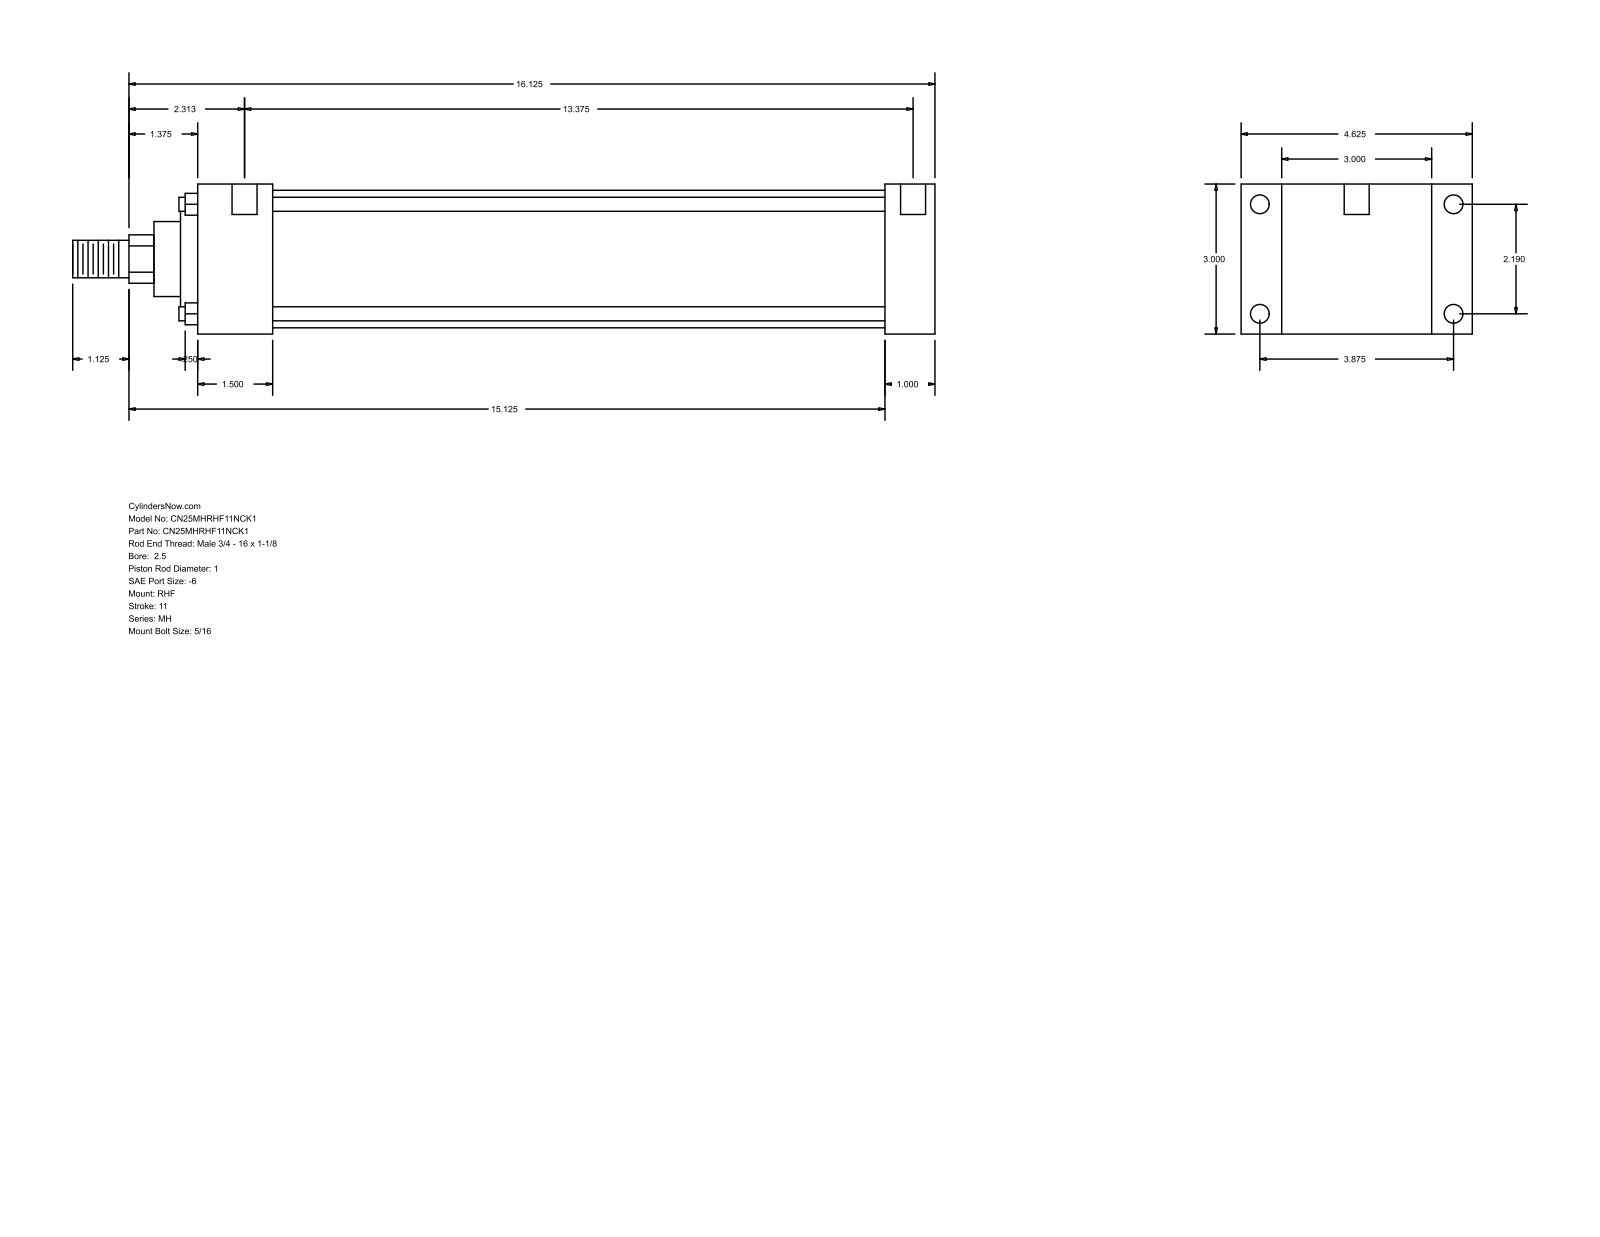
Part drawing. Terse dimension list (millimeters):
name: MH_RHF__0250_1
written by: GSSL Pune (CONFIG_CONTROL_DESIGN)
unit: mm
bodies: 0 solids, 90 faces (61 planar, 29 cylindrical, 0 other)
size: 438.15 × 117.47 × 76.2
holes: 4× ⌀5.56, 4× ⌀9.53, 2× ⌀12.7
bosses: 4× ⌀7.14, 1× ⌀69.85, 1× ⌀60.33, 1× ⌀38.1, 1× ⌀25.4, 1× ⌀19.05
rounds: 1× R12.29
face distances: 76.2, 25.39, 20.64, 96.84, 374.65, 349.26, 117.48, 38.11, 311.15, 336.54
hole spacings: 55.62, 98.42, 113.05, 347.66, 3.18, 4.76, 339.72, 342.9
